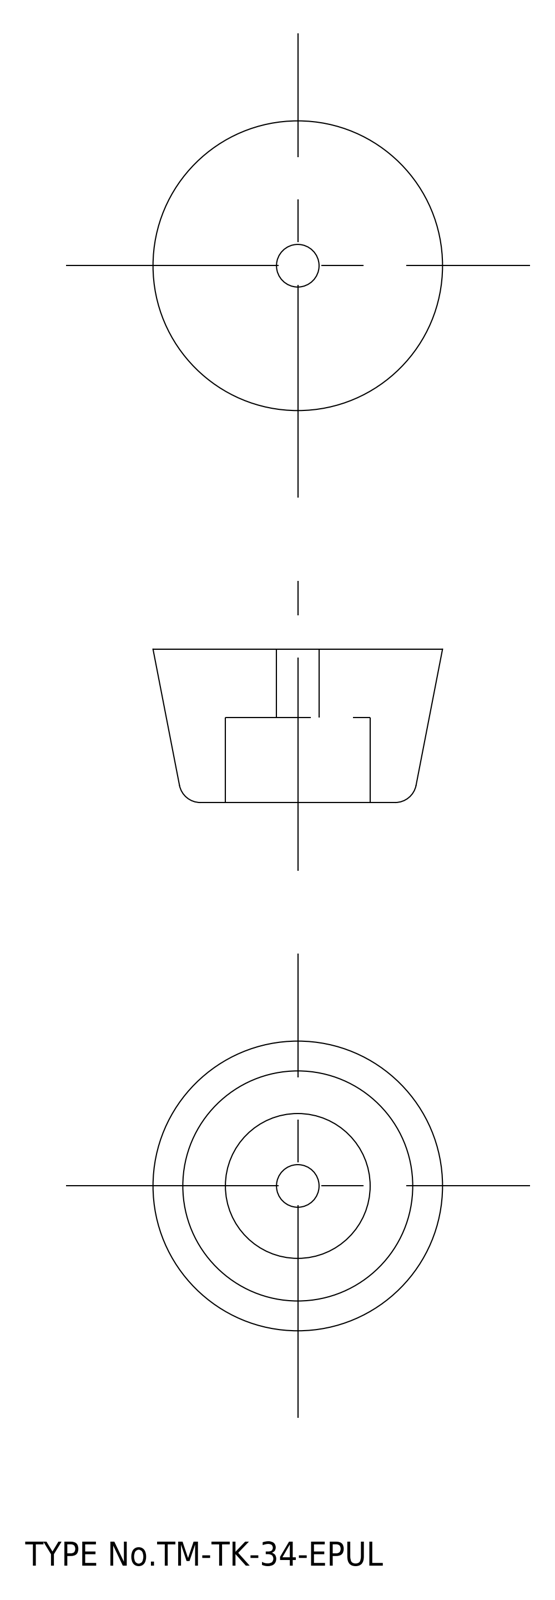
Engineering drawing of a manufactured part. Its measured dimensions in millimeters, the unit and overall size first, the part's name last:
Units: millimetres
Overall size (bounding box): 34 × 34 × 18
Round holes (diameter × count): ⌀5 ×1, ⌀17 ×1, ⌀18 ×1
Main face-to-face distances: 7, 1, 8, 10, 11, 18
Volume: 10 738 mm³ · Surface area: 4 439 mm²
Bodies: 2 solids, 20 faces (6 planar, 10 cylindrical, 4 other)
Part name (STEP PRODUCT): washer; rubber foot
STEP written by: spGate 15.6.1 (AUTOMOTIVE_DESIGN)
